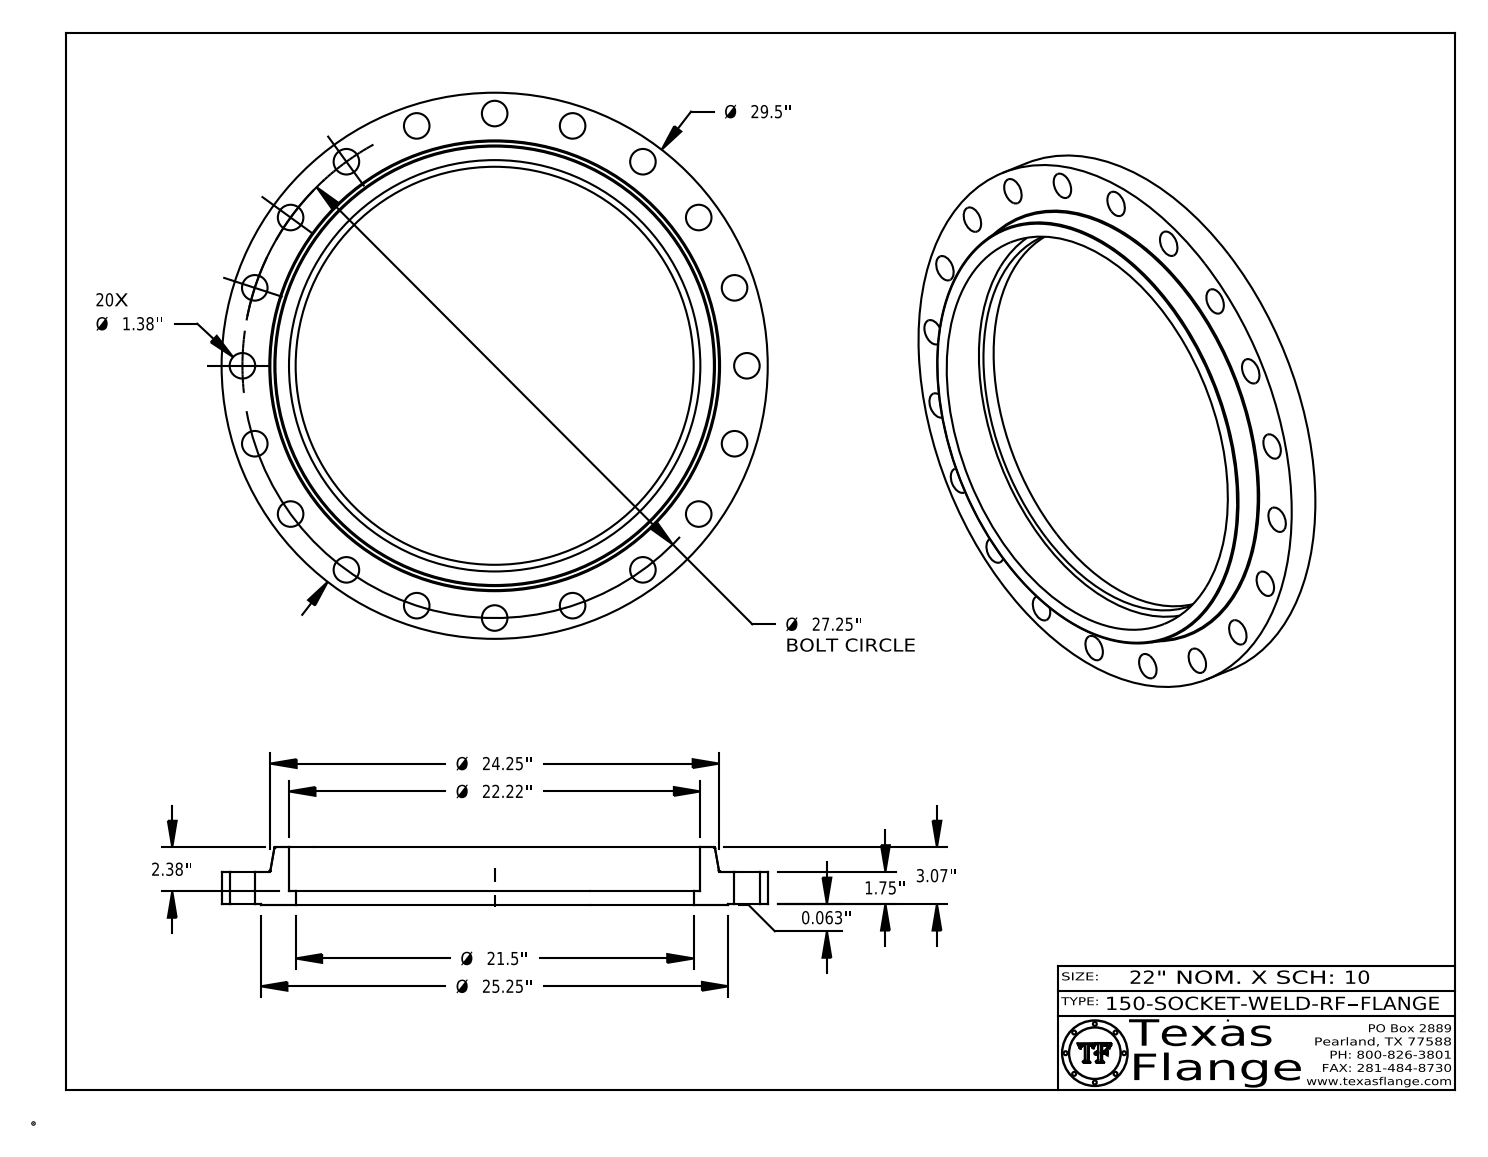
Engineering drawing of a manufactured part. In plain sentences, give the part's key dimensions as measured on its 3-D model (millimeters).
The part is named "150-SOCKET-WELD-RF". Its 3-D file was written by "CATIA V5 STEP AP214 (AUTOMOTIVE_DESIGN)". It is 1 solid with 444 faces: 370 planar, 68 cylindrical and 6 other. Overall it measures 749.3 by 749.3 by 79.6 millimeters. Its volume is 9 455 000 cubic millimeters and its surface area 772 900 square millimeters. Round holes: 20 of diameter 35.1, 1 of diameter 12.6, 1 of diameter 546.1, 1 of diameter 564.4. Round bosses or shafts: 8 of diameter 0.8, 1 of diameter 749.3, 1 of diameter 641.4, 1 of diameter 9.9. The main face-to-face distances are 44.5, 1.6, 46.1, 79.6, 78, 33.5, 19.1, 17.5, 26.9, 60.5. The hole center spacings are 346.1, 489.4, 658.3, 213.9, 314.2, 108.3, 406.8, 560.
